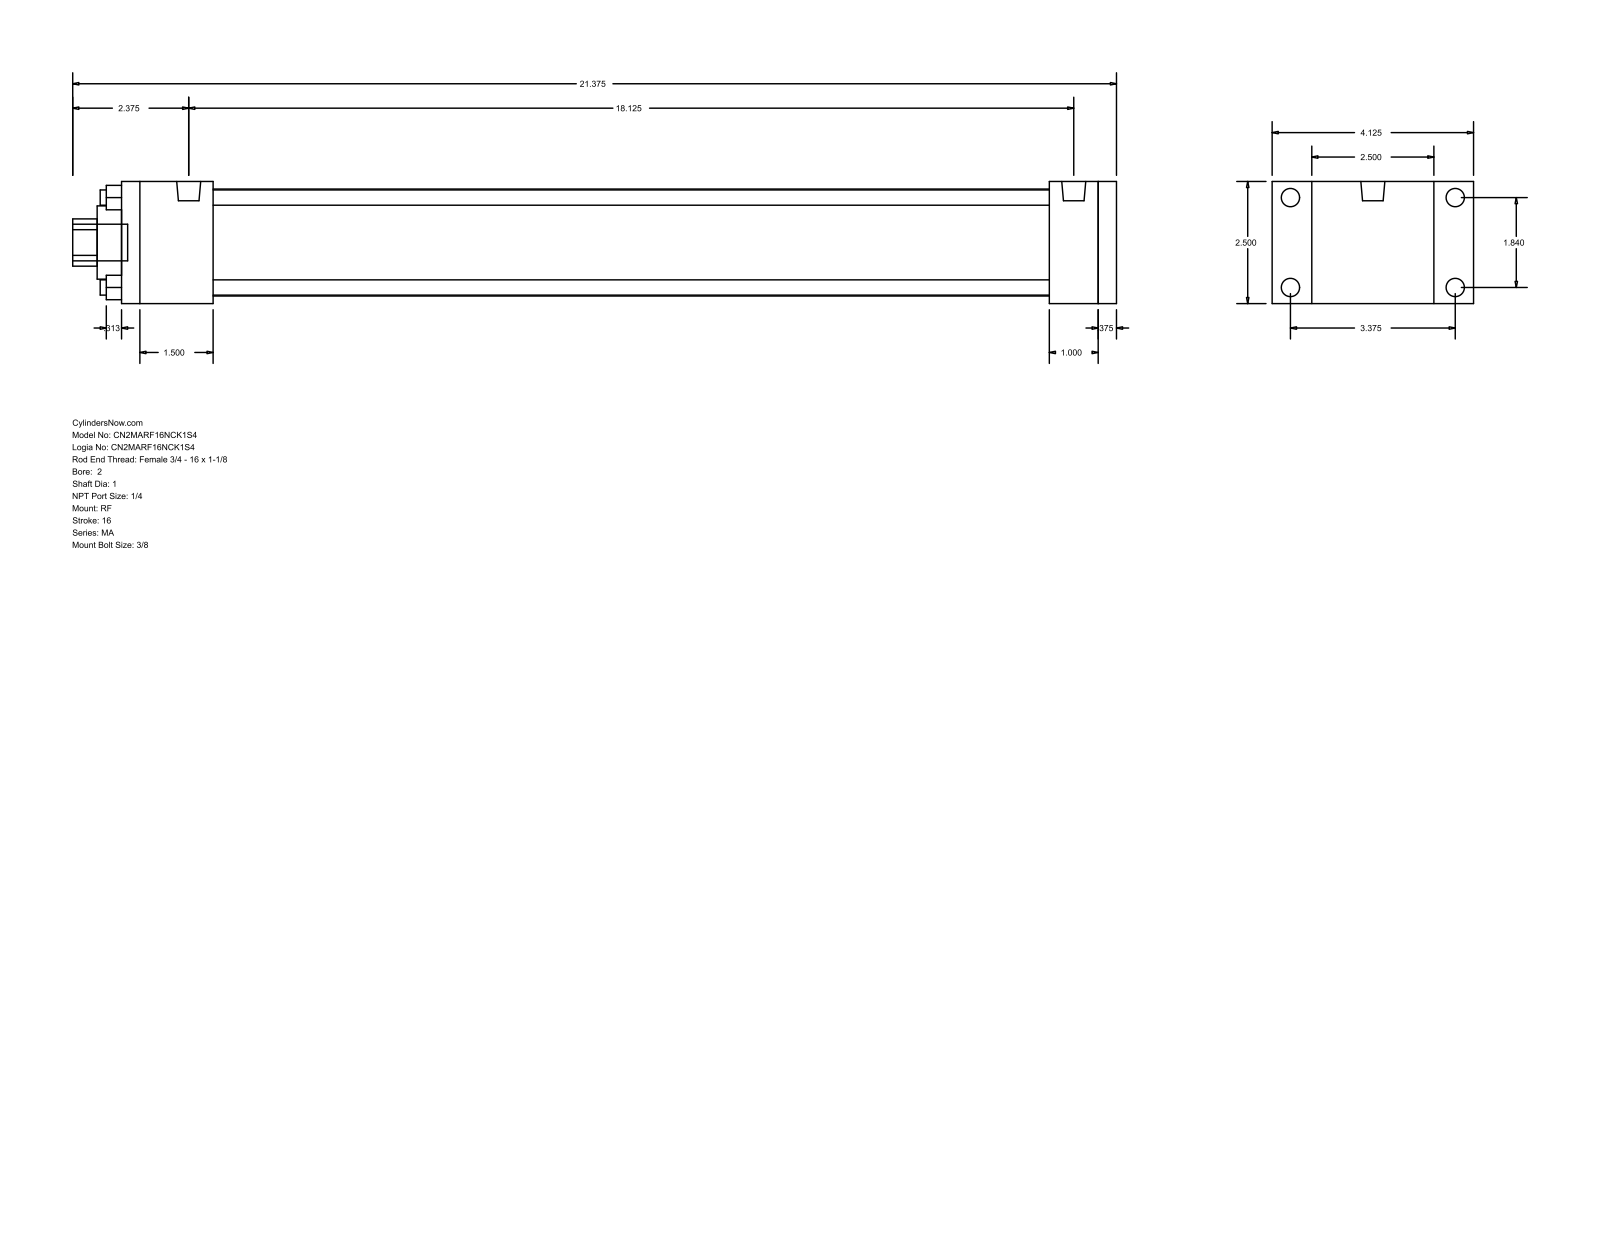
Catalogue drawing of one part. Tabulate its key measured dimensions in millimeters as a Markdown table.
| quantity | value |
| --- | --- |
| part name | MA_RF__0200_1 |
| STEP written by | GSSL Pune (CONFIG_CONTROL_DESIGN) |
| units | millimeters |
| bodies | 0 solids, 92 faces (64 planar, 28 cylindrical, 0 other) |
| overall size | 542.92 × 104.78 × 63.5 |
| round holes (diameter × count) | 7.94 × 4, 25.4 × 1, 38.1 × 1, 55.63 × 1 |
| round bosses / shafts (diameter × count) | 9.53 × 4, 7.94 × 4, 12.49 × 2, 19.05 × 1 |
| partial cylindrical surfaces (radius × count) | 12.29 × 1 |
| main face-to-face distances | 63.5, 508, 9.52, 517.52, 25.4, 20.64, 12.7, 47.63, 460.37, 469.89 |
| hole center spacings | 33.05, 46.74, 66.1 |
